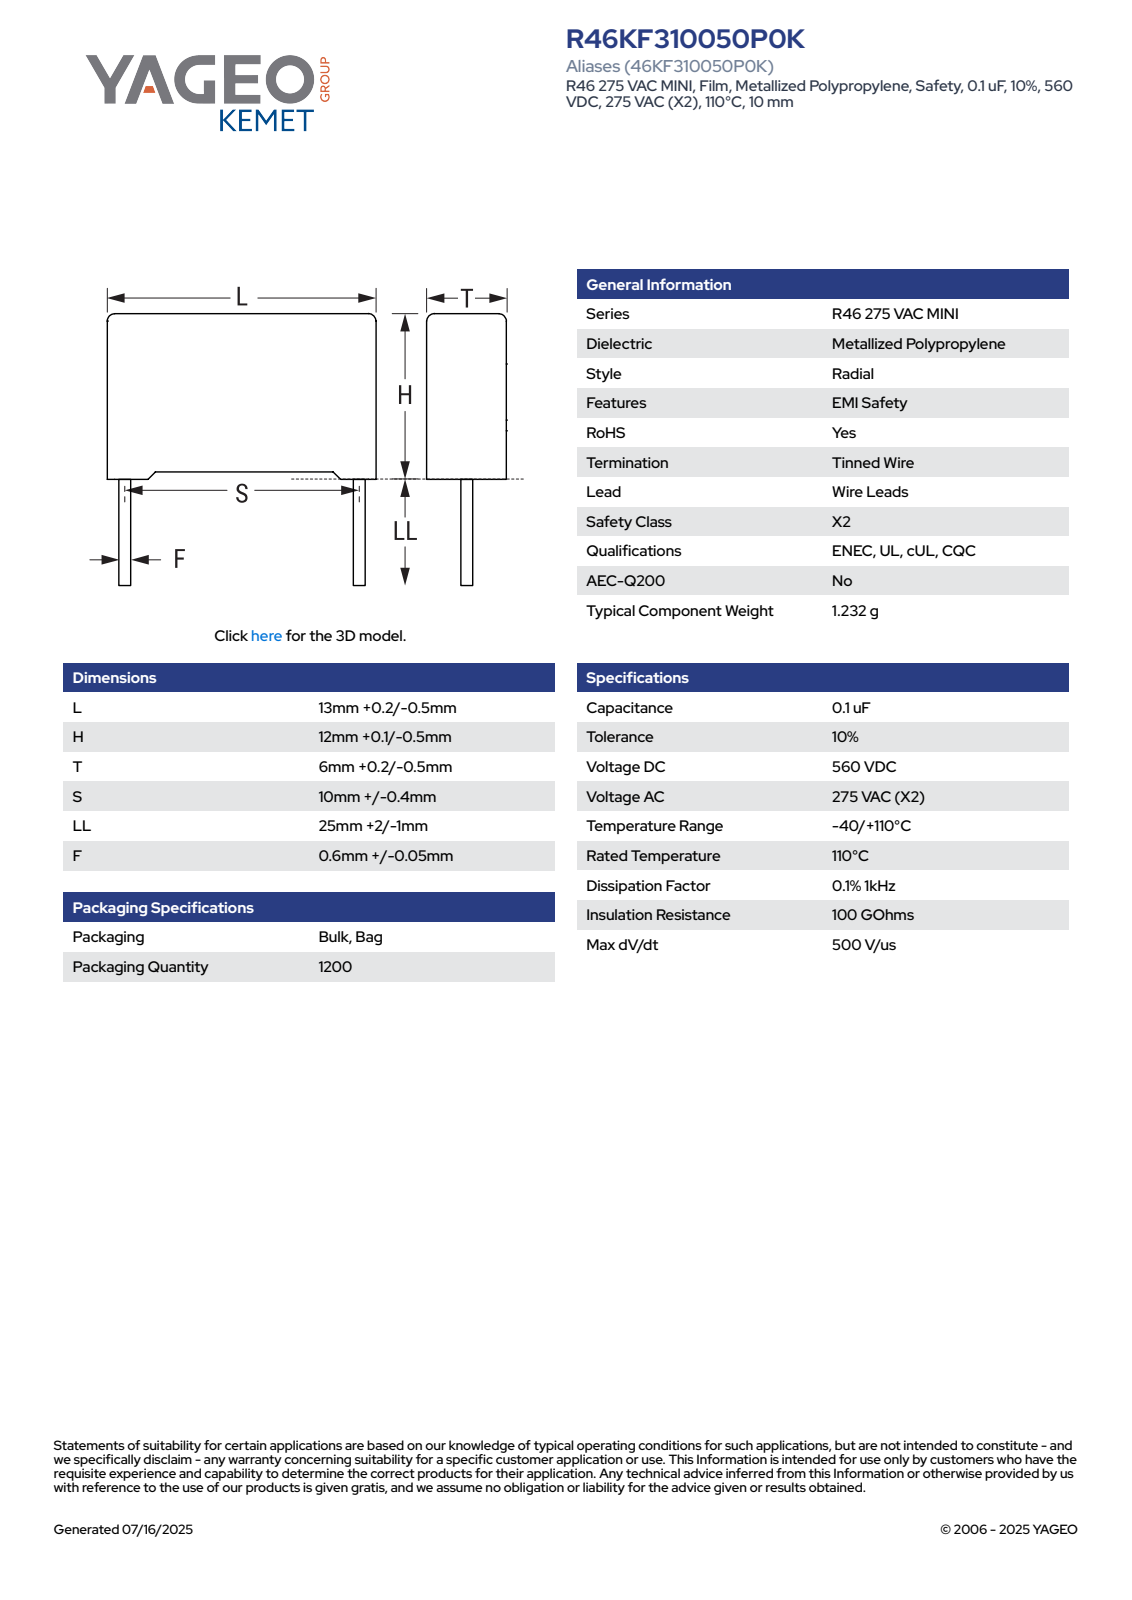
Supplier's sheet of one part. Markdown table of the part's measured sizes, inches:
| quantity | value |
| --- | --- |
| part name | CFR_RB2_13X12X6_L13.2H12.1T6.2S10LL27F0.65 |
| STEP written by | SolidWorks 2021 (AUTOMOTIVE_DESIGN) |
| units | inches |
| bodies | 4 solids, 85 faces (77 planar, 8 cylindrical, 0 other) |
| overall size | 1.539 × 0.52 × 0.244 |
| volume | 0.058 in³ |
| surface area | 1.19 in² |
| round bosses / shafts (diameter × count) | 0.026 × 2 |
| partial cylindrical surfaces (radius × count) | 0.02 × 4 |
| main face-to-face distances | 0.244, 0.52, 0.447, 0.017, 0.227, 0.03, 0.476, 0.502, 0.209, 0.017 |
